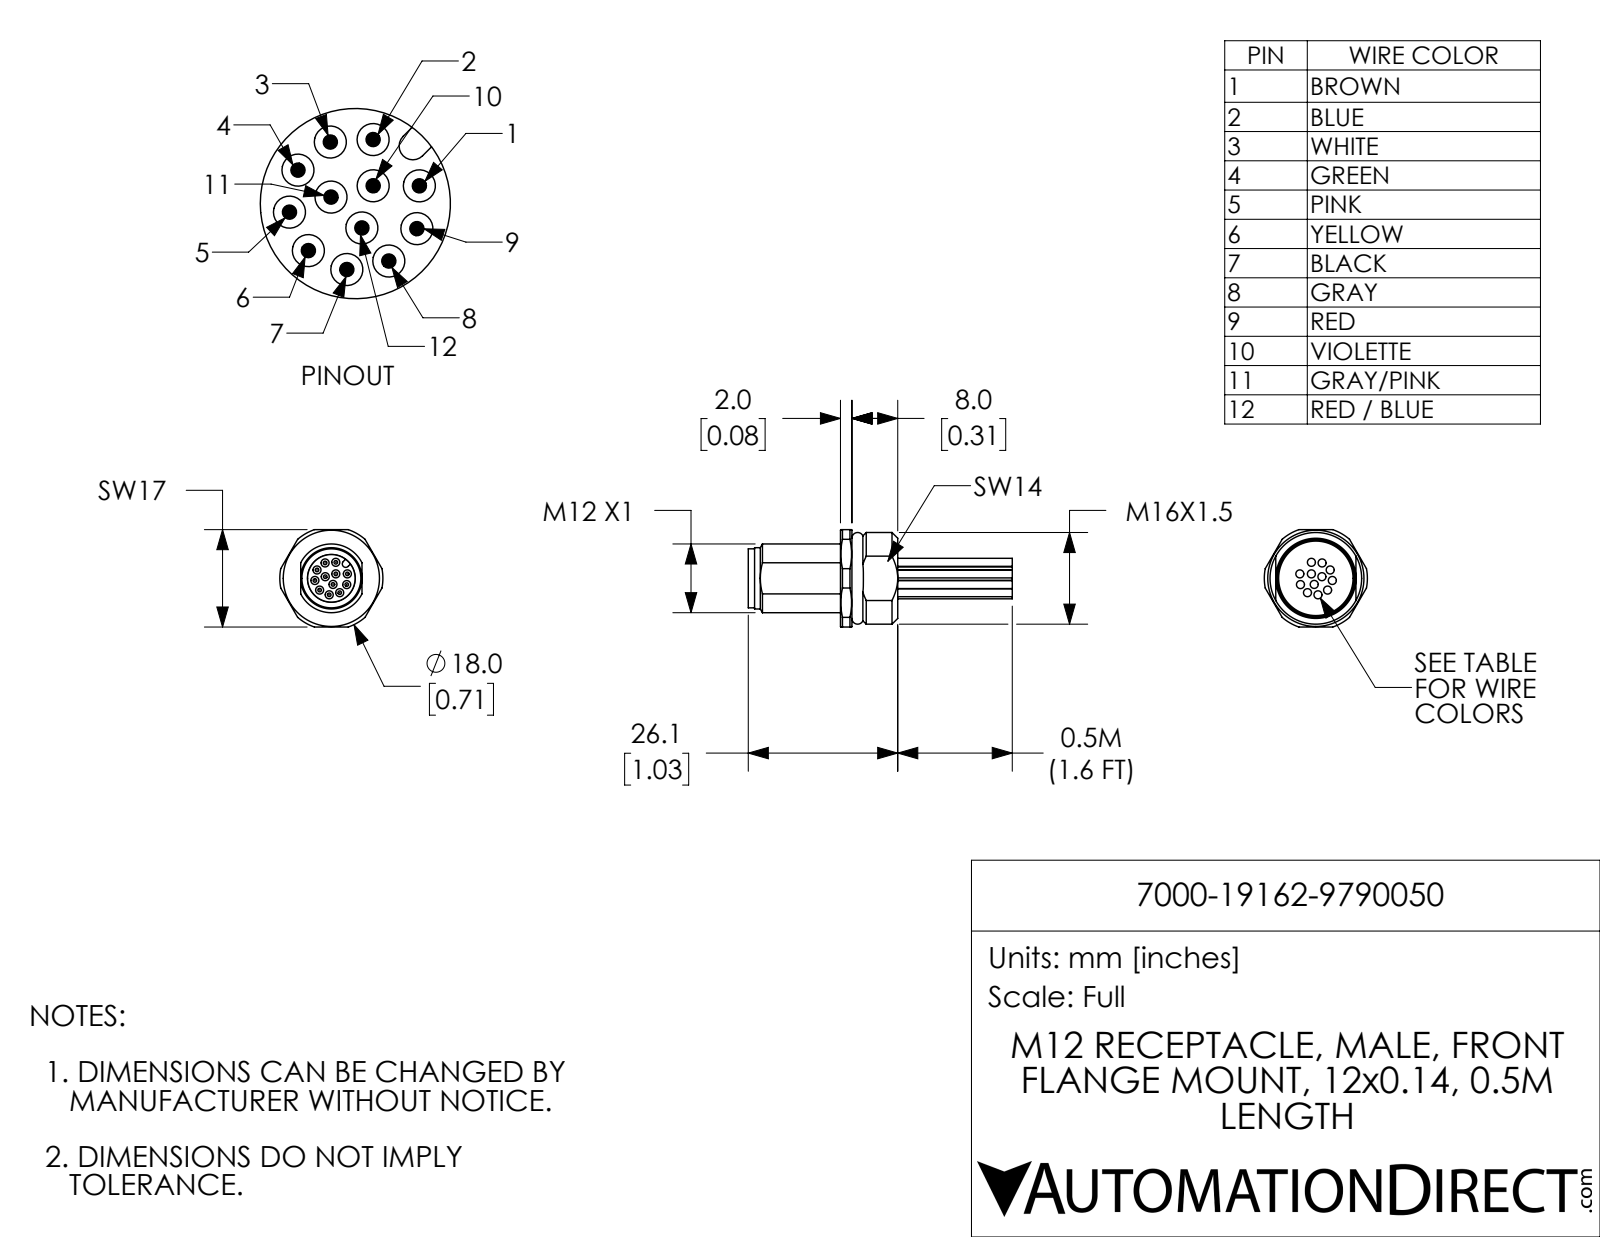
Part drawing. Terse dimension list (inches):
name: 7000-19162-9790050
written by: SolidWorks 2017 (AUTOMOTIVE_DESIGN)
unit: in
bodies: 1 solid, 188 faces (56 planar, 92 cylindrical, 40 other)
size: 1.815 × 0.709 × 0.669
volume: 0.212 in³; area: 4.972 in²
holes: 12× ⌀0.055, 1× ⌀0.327, 1× ⌀0.512
bosses: 12× ⌀0.024, 1× ⌀0.421, 1× ⌀0.406
rounds: 1× R0.024, 1× R0.236, 1× R0.315, 1× R0.354
face distances: 0.354, 0.065, 0.486, 0.421, 0.276, 0.079, 0.551, 0.669, 0.638, 0.362
hole spacings: 0.114, 0.074, 0.139, 0.191, 0.043, 0.14, 0.073, 0.074
